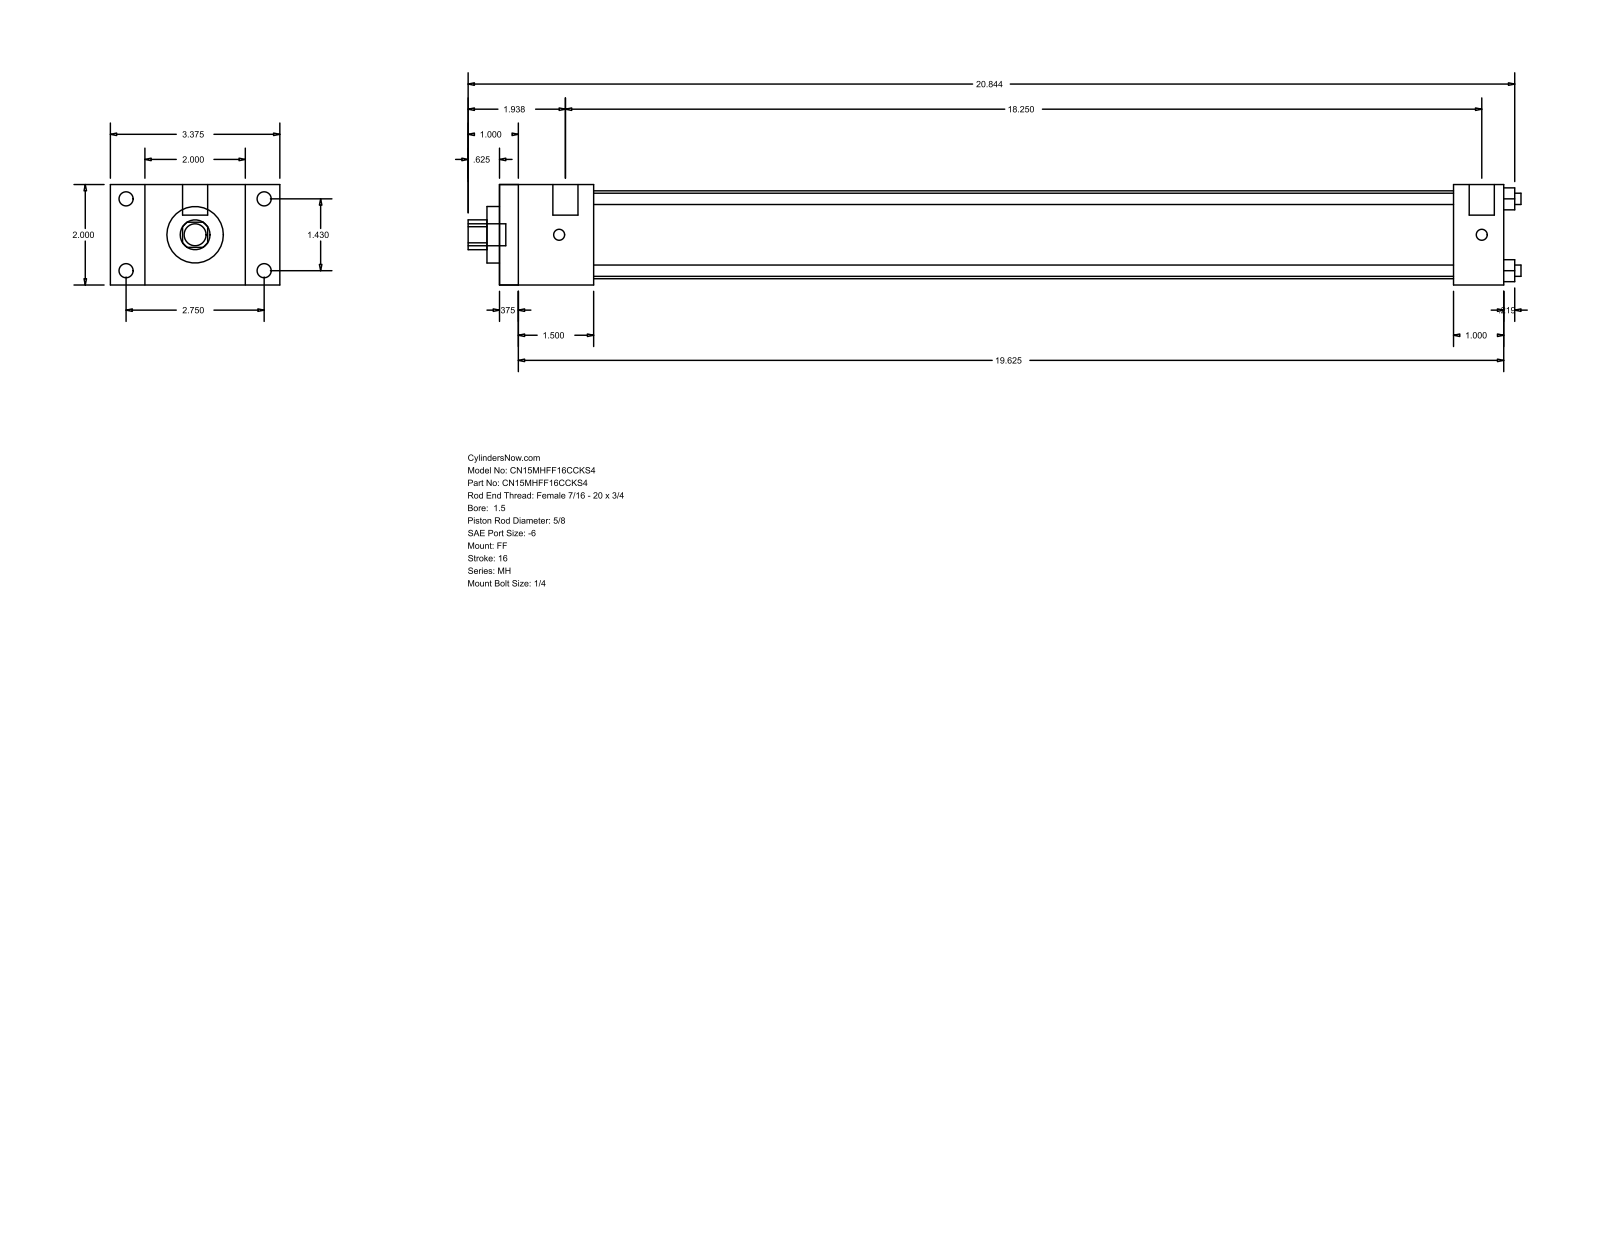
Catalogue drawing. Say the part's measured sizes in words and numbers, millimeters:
The part is named "MH_FF__0150_0.625". Its 3-D file was written by "GSSL Pune (CONFIG_CONTROL_DESIGN)". It is 0 solids with 92 faces: 64 planar, 28 cylindrical and 0 other. Overall it measures 532.61 by 85.72 by 50.8 millimeters. Round holes: 4 of diameter 5.71, 1 of diameter 15.88, 1 of diameter 28.57, 1 of diameter 44.45. Round bosses or shafts: 4 of diameter 7.14, 4 of diameter 5.56, 2 of diameter 12.7, 1 of diameter 11.11. Partial cylindrical surfaces (rounded edges, fillets, slot ends): 1 of radius 7.54. The main face-to-face distances are 50.8, 508, 9.52, 498.48, 25.4, 17.46, 68.26, 47.62, 38.1, 460.38. The hole center spacings are 25.68, 36.32, 51.36.
